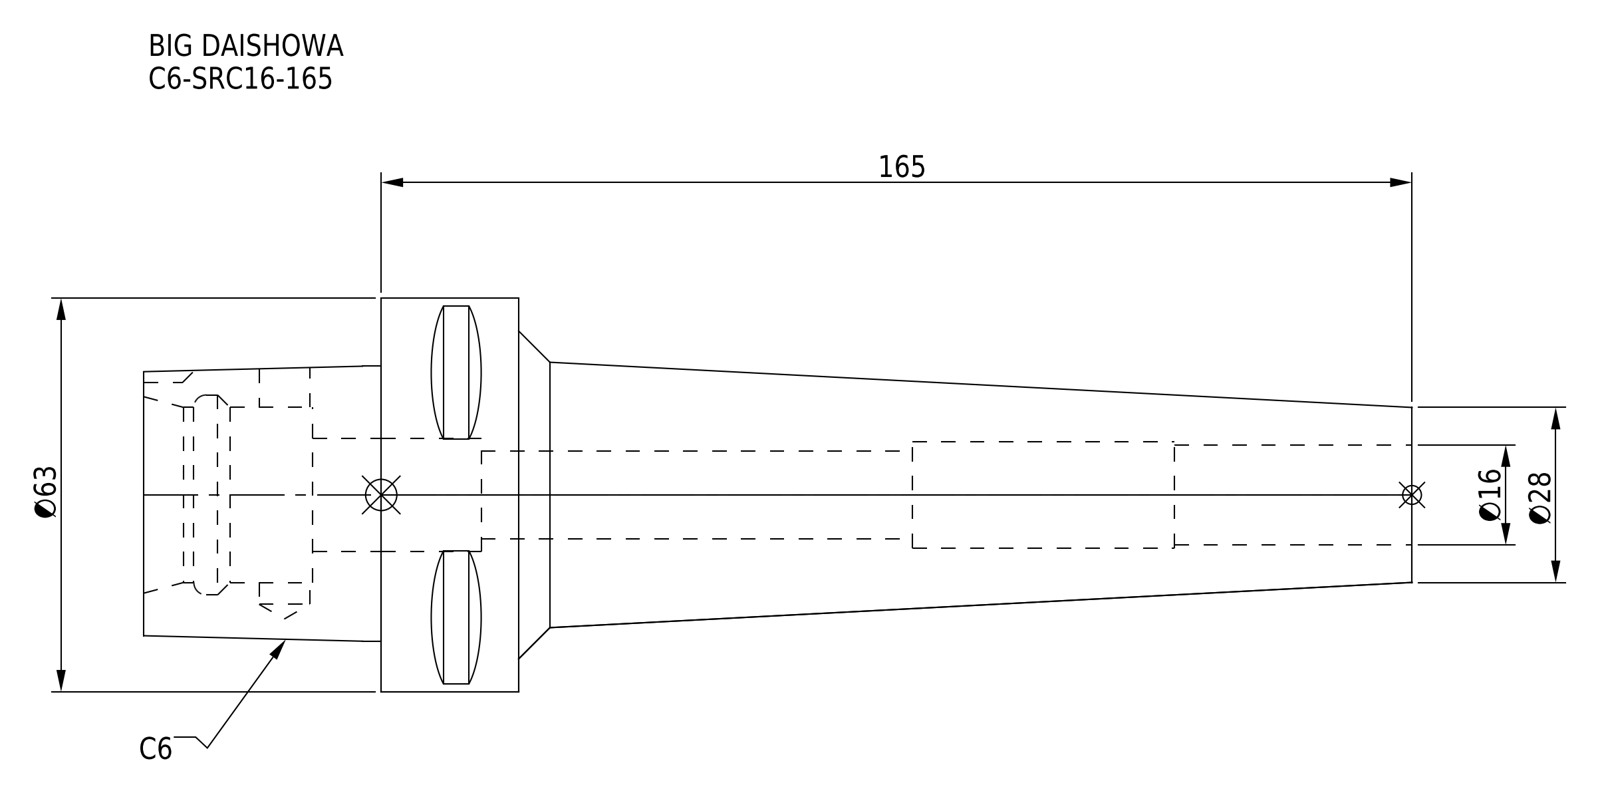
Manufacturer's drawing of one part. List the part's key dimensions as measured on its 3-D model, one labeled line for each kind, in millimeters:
Part name (STEP PRODUCT): C6-SRC16-165
STEP written by: CREO PARAMETRIC BY PTC INC, 2016380 (AUTOMOTIVE_DESIGN)
Units: millimetres
Bodies: 1 solid, 65 faces (30 planar, 21 cylindrical, 14 other)
Overall size (bounding box): 203 × 63 × 63
Volume: 214 099 mm³ · Surface area: 41 885 mm²
Round holes (diameter × count): ⌀8.1 ×1, ⌀14 ×1, ⌀16 ×1, ⌀17 ×1, ⌀18 ×1, ⌀28 ×1, ⌀32 ×1
Round bosses / shafts (diameter × count): ⌀63 ×1
Partial cylindrical surfaces — rounded edges, fillets, slot ends (radius × count): R5 ×1
Main face-to-face distances: 22, 38, 60, 27, 165, 143, 203, 176, 33, 11
